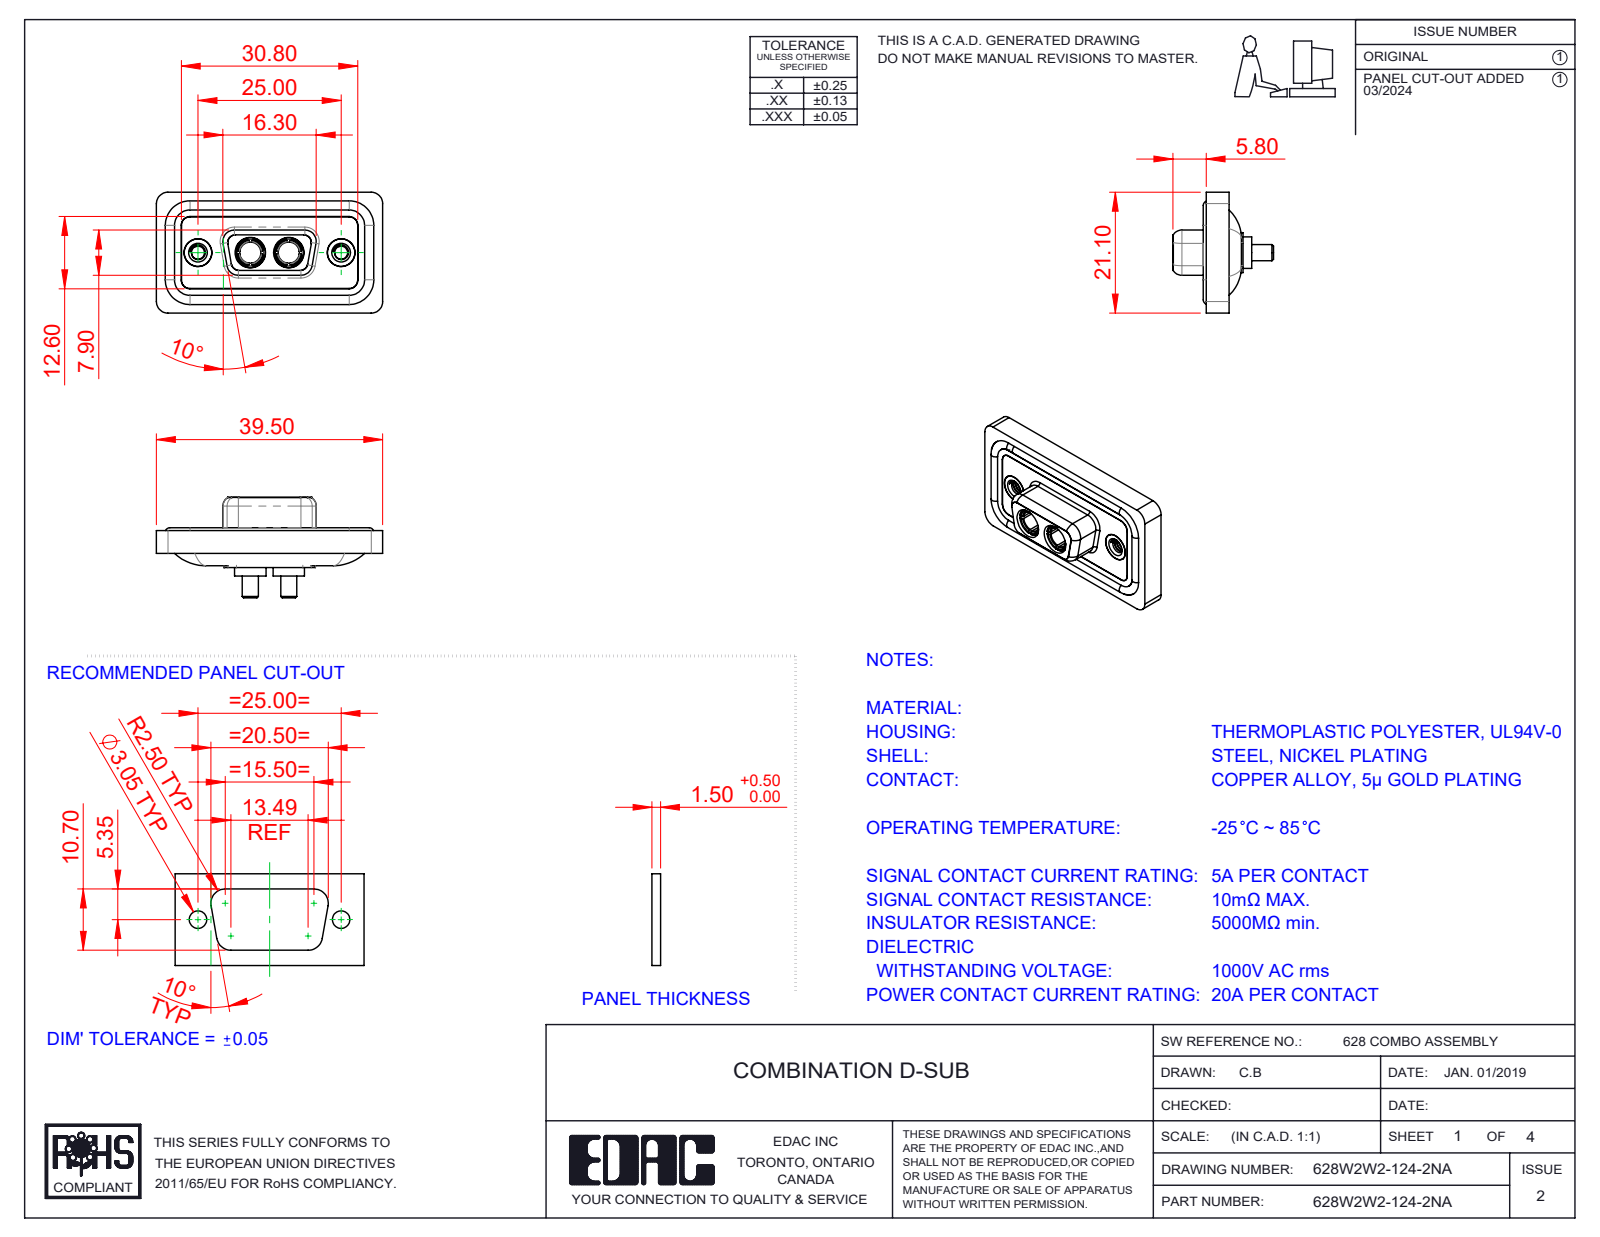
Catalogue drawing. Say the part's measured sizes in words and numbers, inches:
The part is named "628Combo Shell Front_09 Contacts; Power Socket_20A S; 628Combo Shell Rear_09 Contacts; 628W2W2-124-2NA (+3 more)". Its 3-D file was written by "SolidWorks 2023 (CONFIG_CONTROL_DESIGN)". It is 11 solids with 532 faces: 163 planar, 236 cylindrical and 133 other. Overall it measures 1.555 by 0.831 by 0.691 inches. Its volume is 0.288 cubic inches and its surface area 11.83 square inches. Round holes: 4 of diameter 0.191, 2 of diameter 0.089, 2 of diameter 0.146, 2 of diameter 0.157, 2 of diameter 0.159, 2 of diameter 0.197, 2 of diameter 0.209. Round bosses or shafts: 4 of diameter 0.063, 2 of diameter 0.217, 2 of diameter 0.205, 2 of diameter 0.195, 2 of diameter 0.195, 2 of diameter 0.189, 2 of diameter 0.187, 2 of diameter 0.148. Partial cylindrical surfaces (rounded edges, fillets, slot ends): 22 of radius 0.059, 18 of radius 0.079, 8 of radius 0.053, 8 of radius 0.063, 4 of radius 0.01, 4 of radius 0.02, 4 of radius 0.024, 4 of radius 0.026. The main face-to-face distances are 0.016, 0.071, 0.043, 0.114, 0.02, 0.063, 0.222, 0.293, 0.059, 0.211. The hole center spacings are 0.36, 0.624, 0.265, 0.984.
